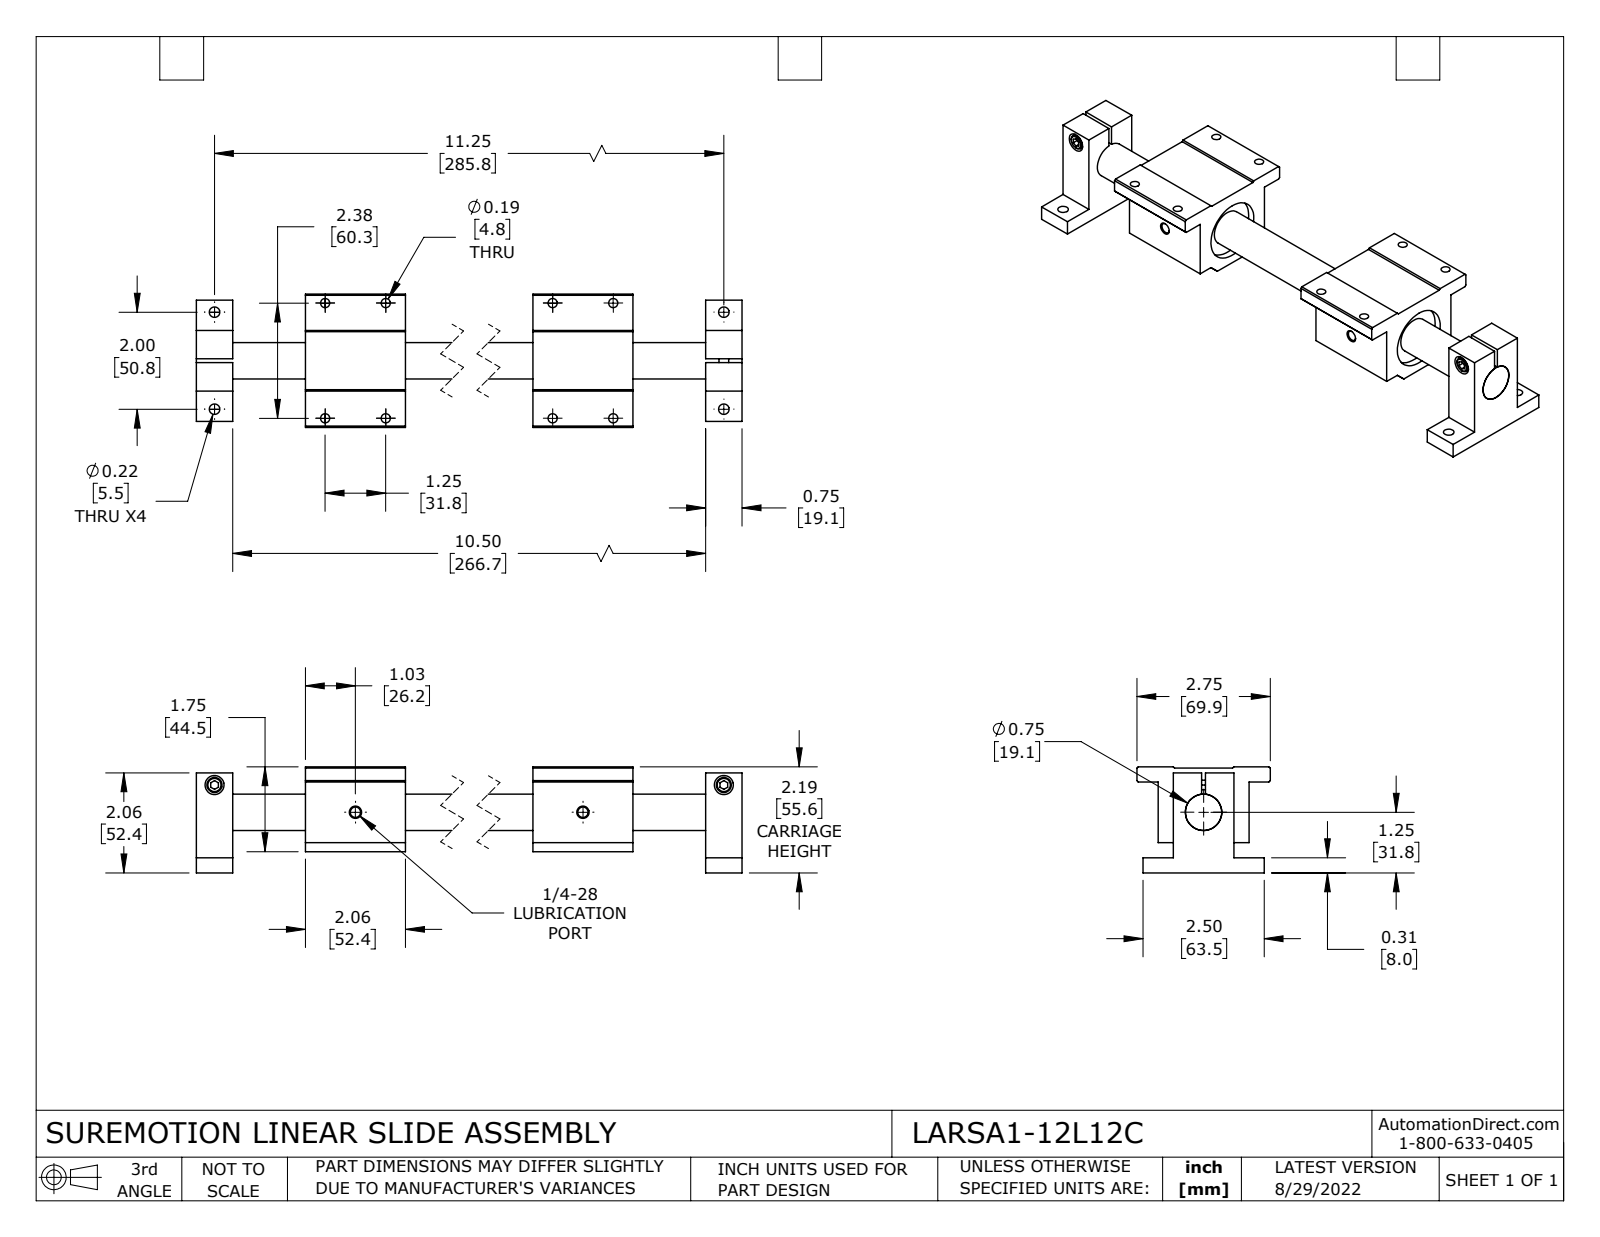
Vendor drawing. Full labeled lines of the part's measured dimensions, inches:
Part name (STEP PRODUCT): LARSA1-12L12C-RAIL; LARSACC-002; LARSA1-12L12C
STEP written by: SolidWorks 2021 (CONFIG_CONTROL_DESIGN)
Units: inches
Bodies: 7 solids, 166 faces (98 planar, 58 cylindrical, 10 other)
Overall size (bounding box): 12 × 2.75 × 2.187
Volume: 20.48 in³ · Surface area: 119.1 in²
Round holes (diameter × count): ⌀0.188 ×8, ⌀0.218 ×4, ⌀0.213 ×2, ⌀0.394 ×2, ⌀0.75 ×1, ⌀1.25 ×1
Round bosses / shafts (diameter × count): ⌀0.312 ×2
Main face-to-face distances: 1.563, 0.75, 2.063, 5.437, 1.75, 0.313, 1.876, 11.25, 0.028, 0.313
Hole centre spacings: 1.25, 2.289, 2.376, 2.684, 3.161, 3.537, 4.154, 5.437
